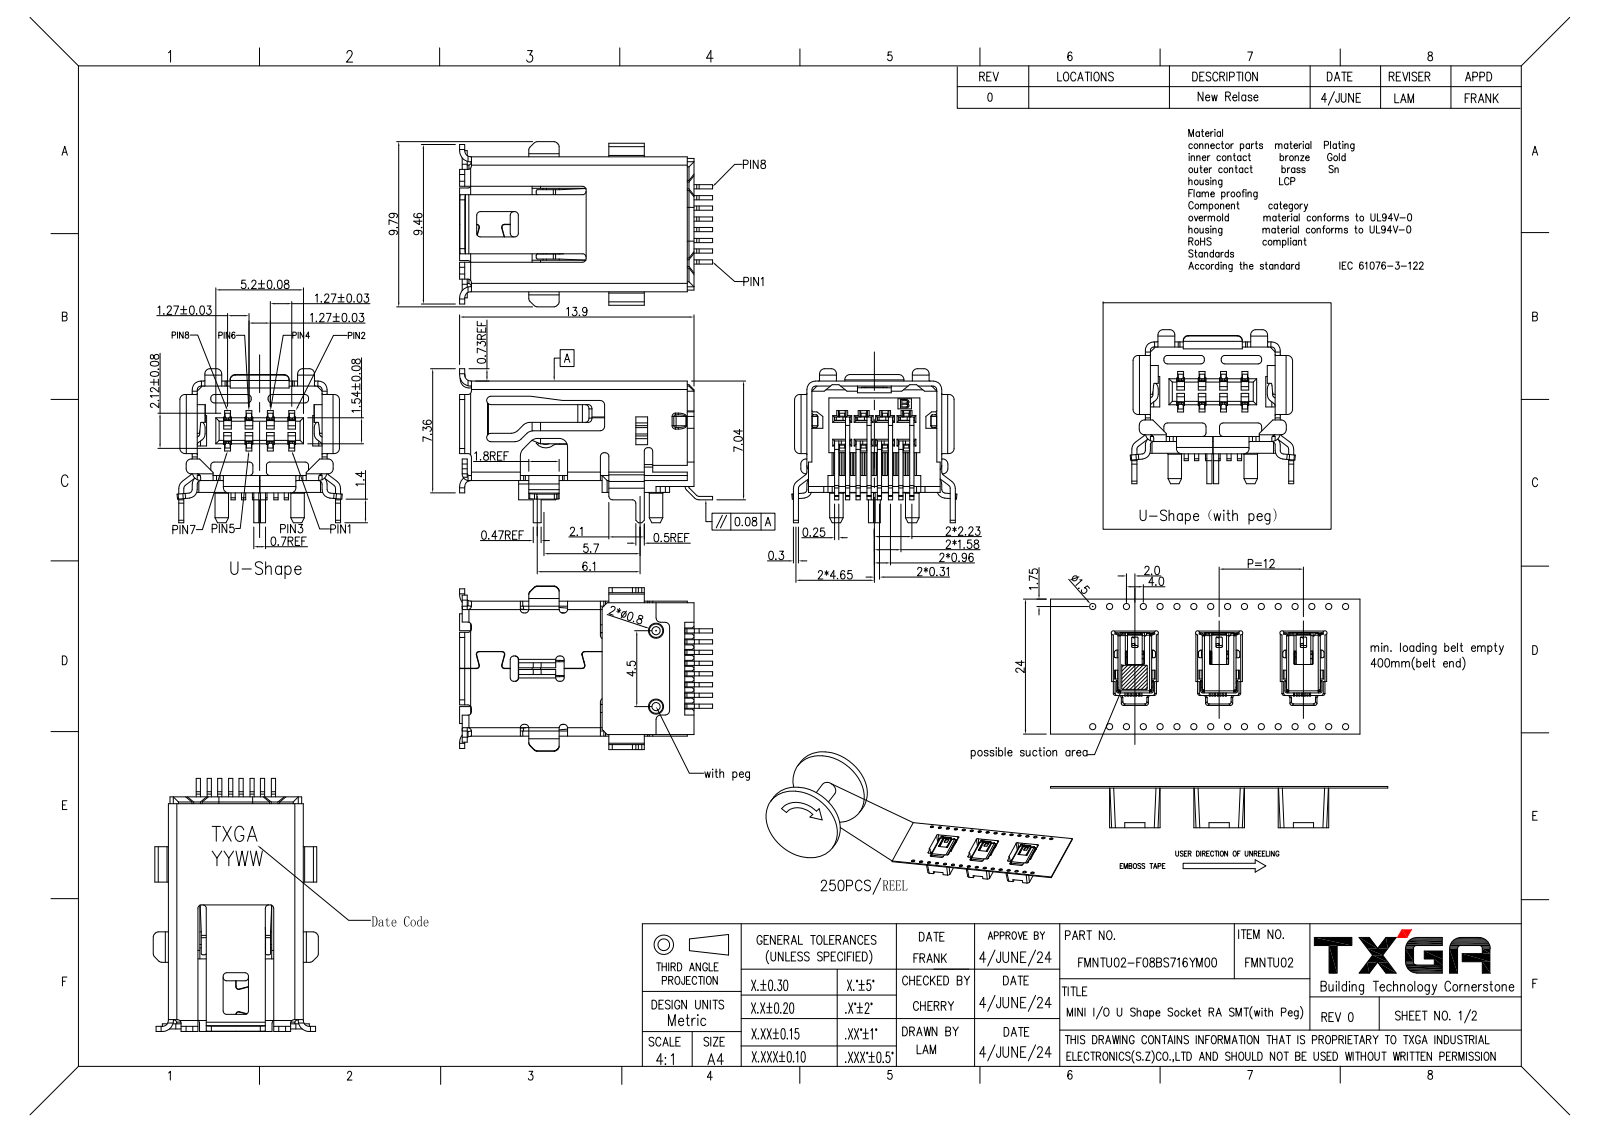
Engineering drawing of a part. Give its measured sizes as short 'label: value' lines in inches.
name: FMINI-SURA1XXX-000
written by: PRO/ENGINEER BY PARAMETRIC TECHNOLOGY CORPORATION, 2010280 (CONFIG_CONTROL_DESIGN)
unit: in
bodies: 1 solid, 1563 faces (1143 planar, 388 cylindrical, 32 other)
size: 0.591 × 0.385 × 0.359
volume: 0.011 in³; area: 1.928 in²
bosses: 2× ⌀0.031
rounds: 91× R0.008, 65× R0.004, 30× R0.02, 24× R0.006, 20× R0.012, 12× R0.01, 9× R0.016, 8× R0.007
face distances: 0.22, 0.209, 0.303, 0.232, 0.039, 0.26, 0.248, 0.315, 0.028, 0.291
